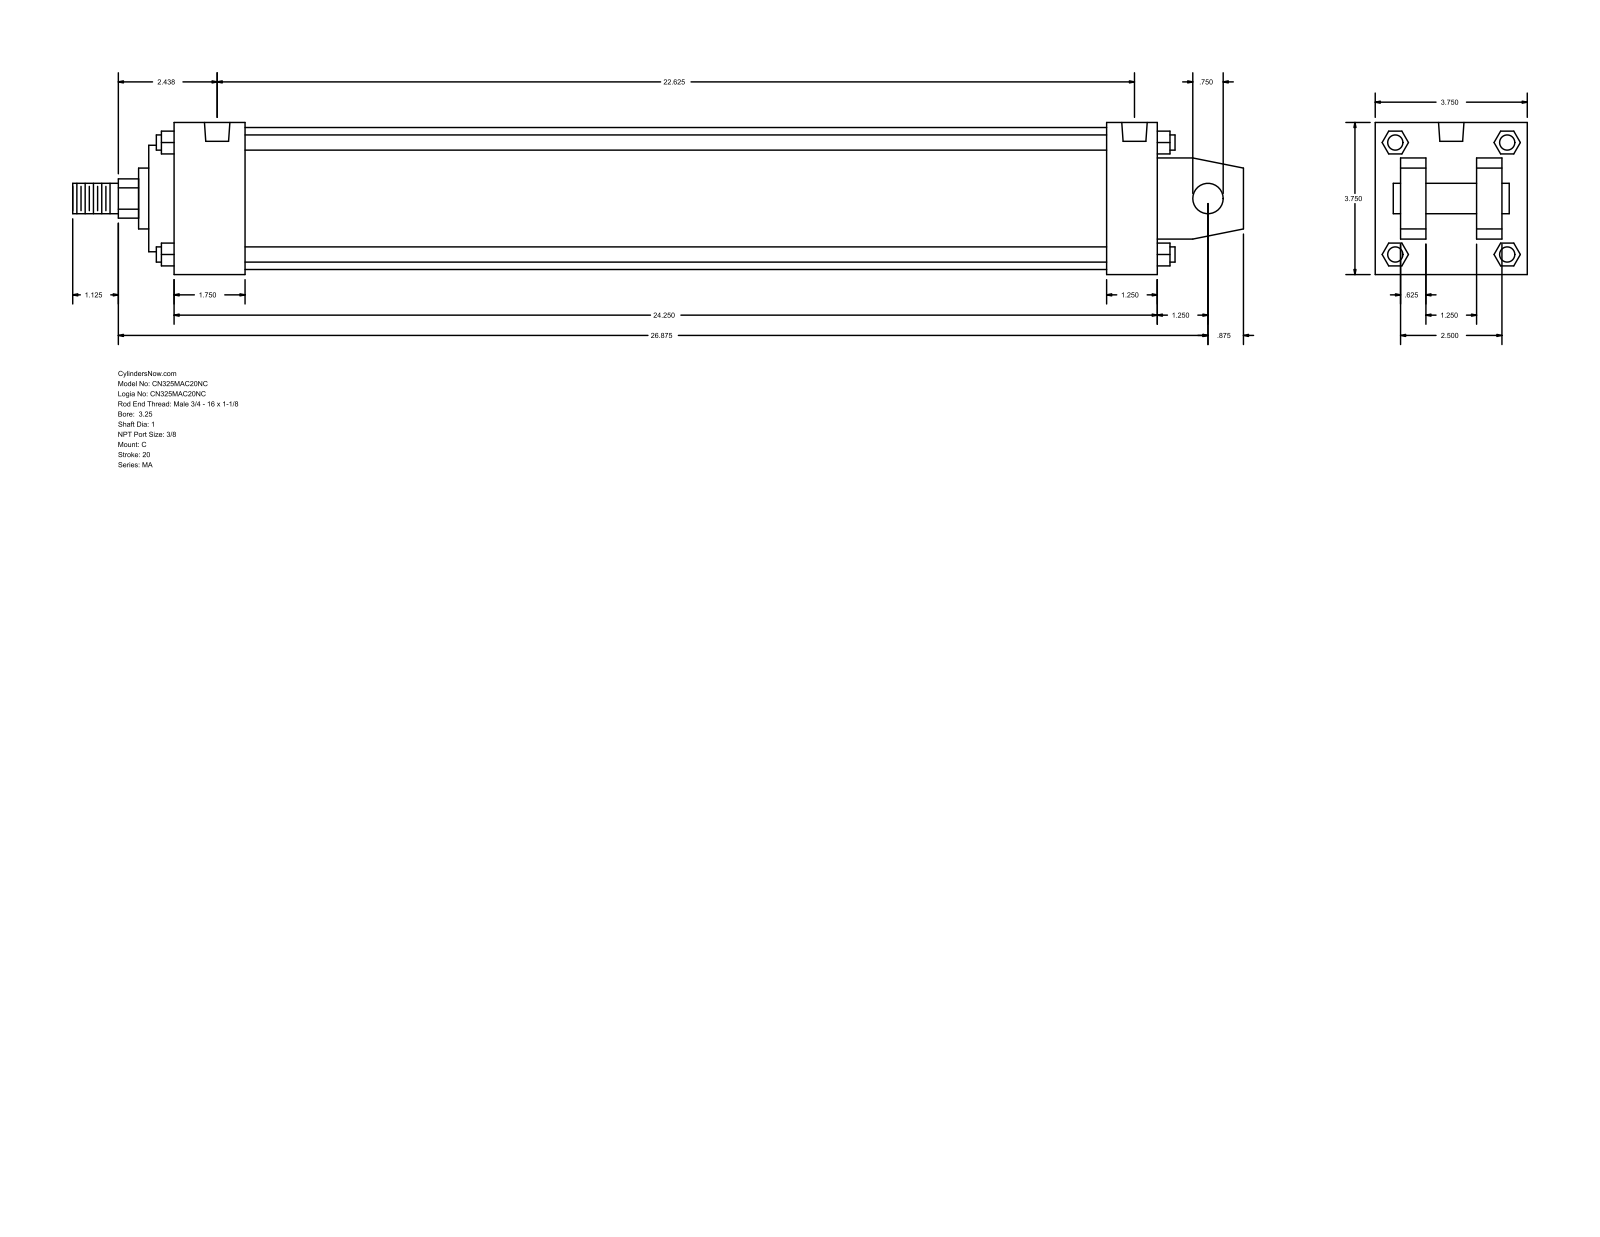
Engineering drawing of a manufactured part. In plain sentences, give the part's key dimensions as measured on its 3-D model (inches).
The part is named "MA_C__0325_1". Its 3-D file was written by "GSSL Pune (CONFIG_CONTROL_DESIGN)". It is 0 solids with 141 faces: 109 planar, 32 cylindrical and 0 other. Overall it measures 28.875 by 3.75 by 3.75 inches. Round holes: 4 of diameter 0.437, 2 of diameter 0.627. Round bosses or shafts: 4 of diameter 0.375, 2 of diameter 0.75, 1 of diameter 3.5, 1 of diameter 2.625, 1 of diameter 1.5, 1 of diameter 1. Partial cylindrical surfaces (rounded edges, fillets, slot ends): 1 of radius 0.484. The main face-to-face distances are 3.75, 0.625, 2.5, 24.25, 1.25, 1.25, 3.125, 1.875, 23, 1.75. The hole center spacings are 0.187, 22.25, 22.438, 22.625.
